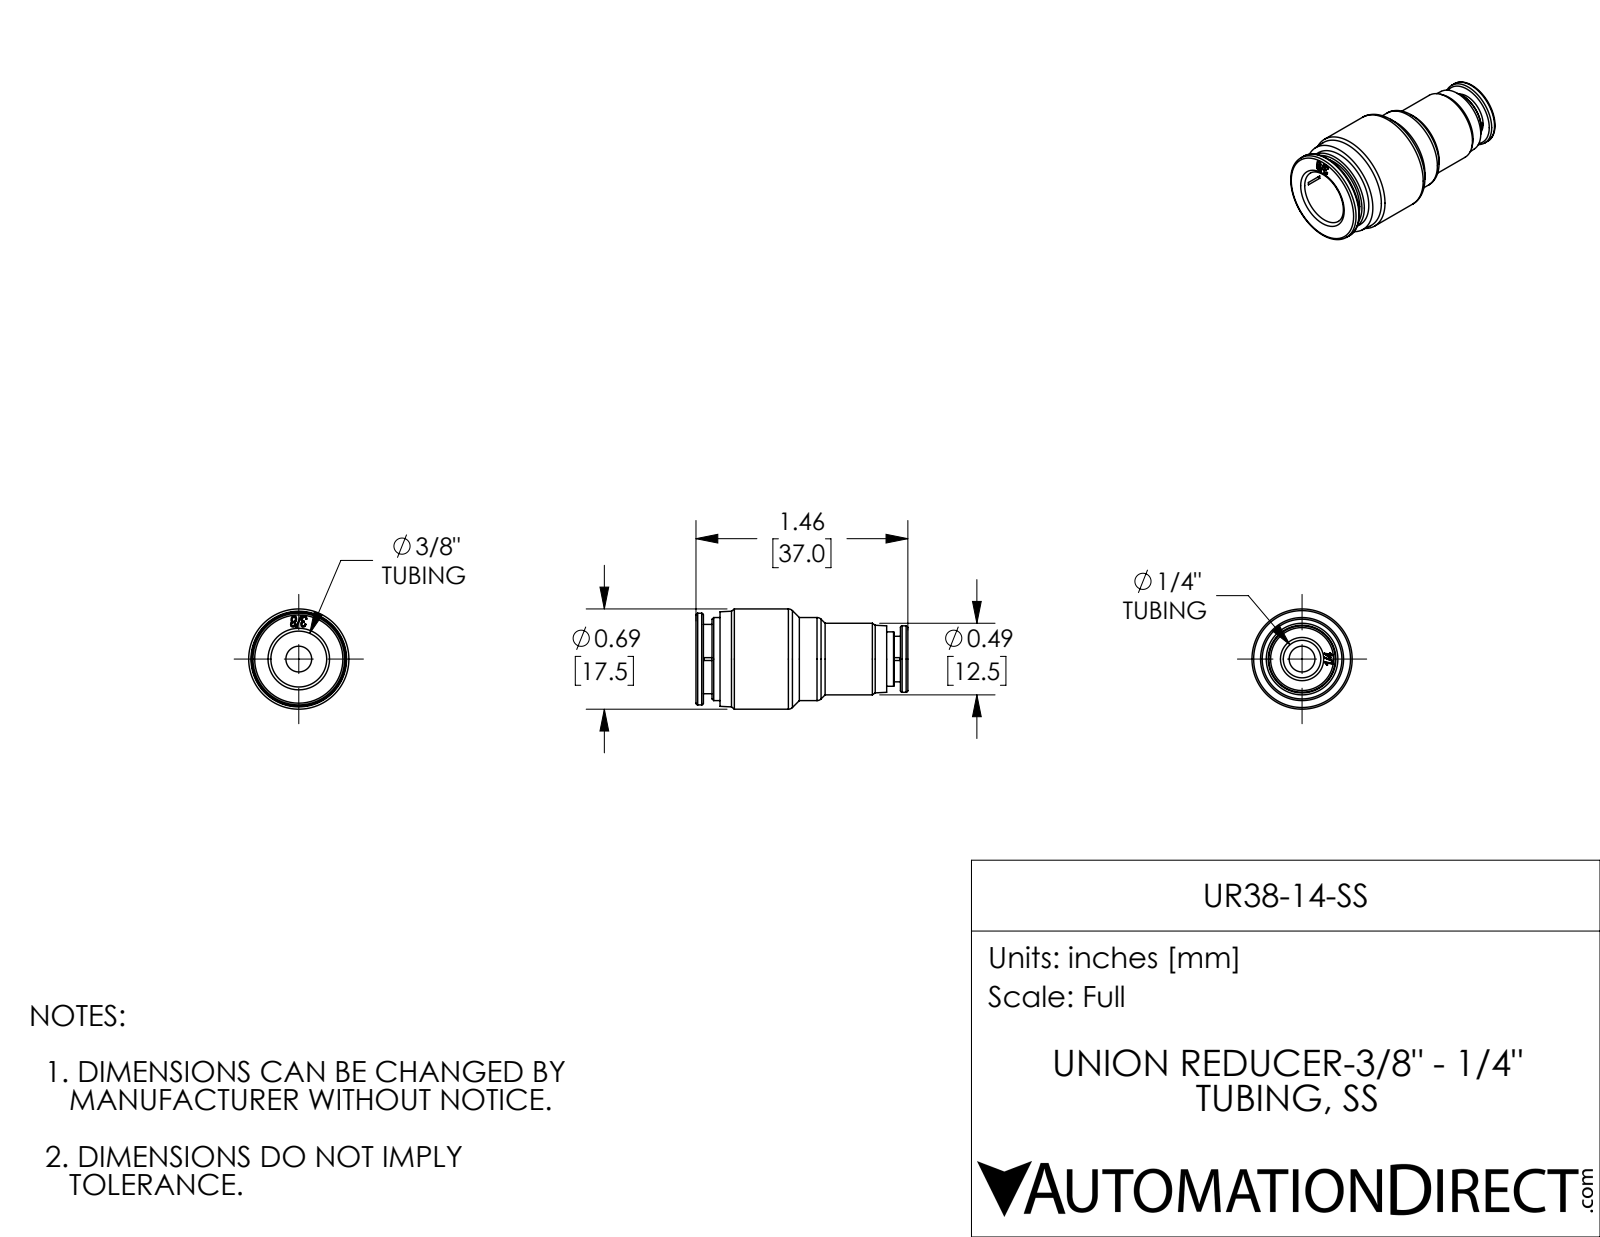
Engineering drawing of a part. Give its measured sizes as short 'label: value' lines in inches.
name: UR38-14-SS
written by: SolidWorks 2017 (AUTOMOTIVE_DESIGN)
unit: in
bodies: 1 solid, 163 faces (63 planar, 26 cylindrical, 74 other)
size: 1.457 × 0.689 × 0.689
volume: 0.25 in³; area: 5.249 in²
holes: 1× ⌀0.177, 1× ⌀0.258, 1× ⌀0.319, 1× ⌀0.384
bosses: 1× ⌀0.689, 1× ⌀0.63, 1× ⌀0.571, 1× ⌀0.492, 1× ⌀0.476, 1× ⌀0.457, 1× ⌀0.374, 1× ⌀0.313
face distances: 0.051, 1.406, 0.787, 0.736, 0.622, 0.165, 0.114, 1.291, 1.457, 0.669
